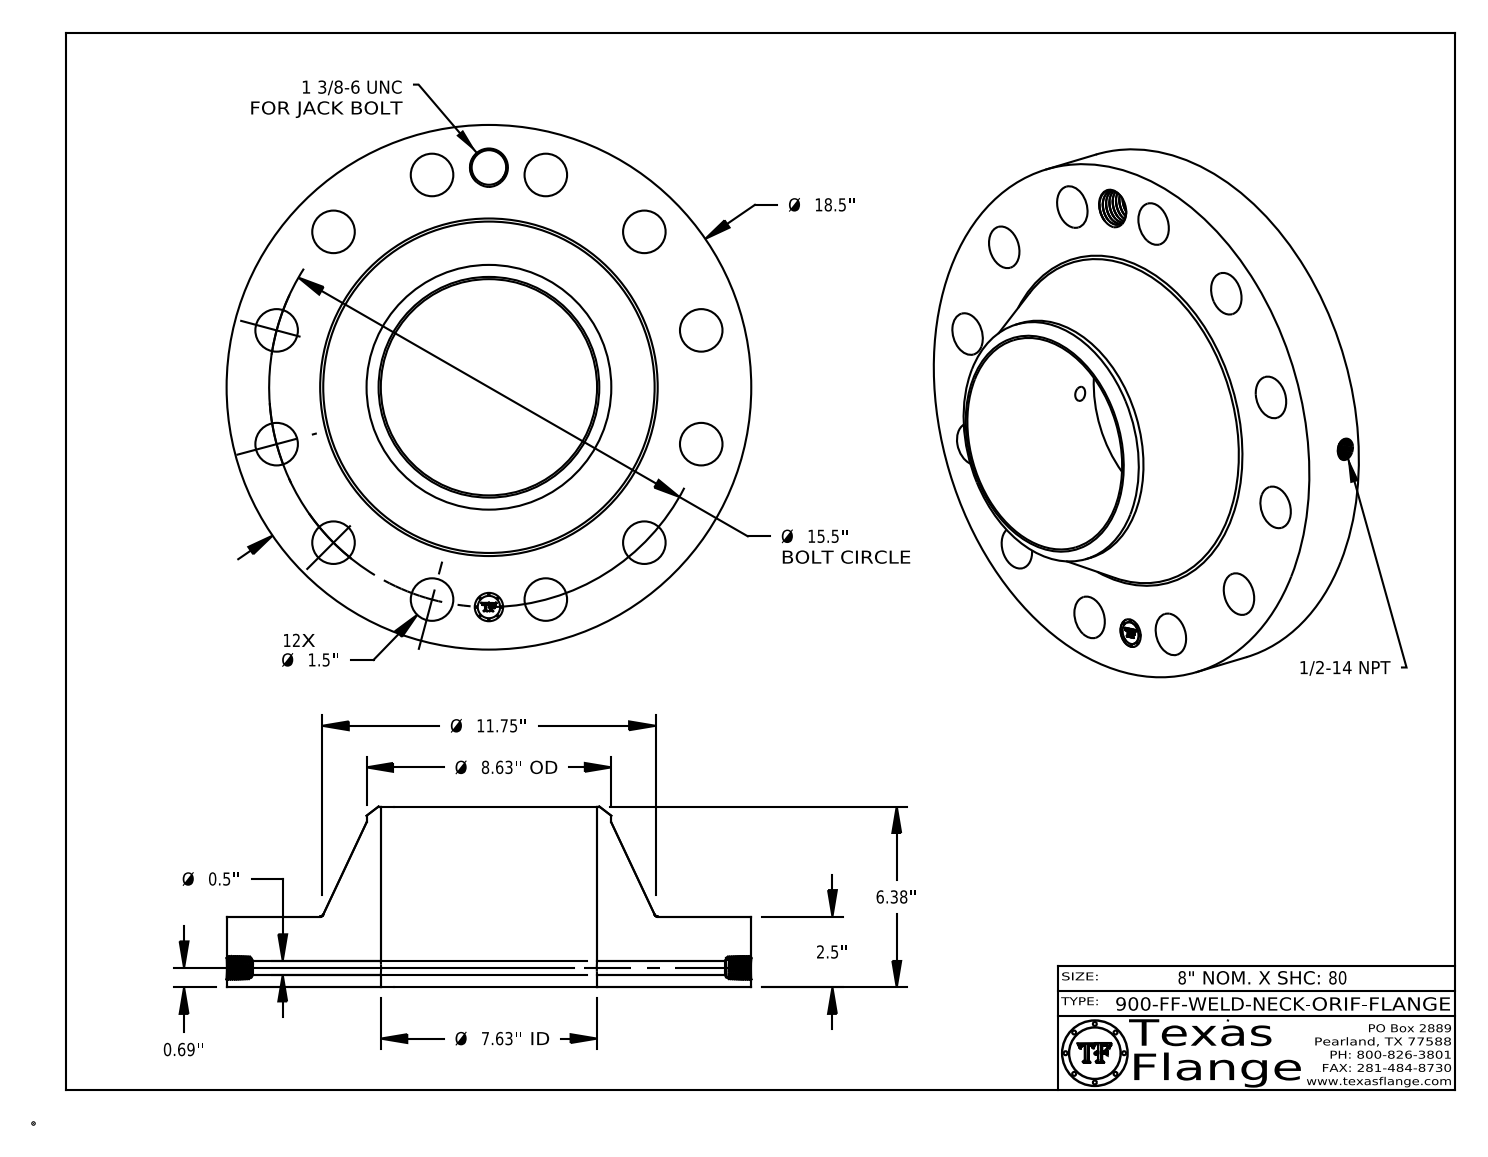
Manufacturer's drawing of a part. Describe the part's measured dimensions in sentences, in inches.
The part is named "900-FF-WELD-NECK". Its 3-D file was written by "CATIA V5 STEP AP214 (AUTOMOTIVE_DESIGN)". It is 1 solid with 774 faces: 368 planar, 100 cylindrical and 306 other. Overall it measures 18.5 by 18.5 by 6.38 inches. Its volume is 625.6 cubic inches and its surface area 951.3 square inches. Round holes: 12 of diameter 1.5, 1 of diameter 0.5, 1 of diameter 0.672, 1 of diameter 1, 1 of diameter 1.219, 1 of diameter 7.625. Round bosses or shafts: 8 of diameter 0.061, 1 of diameter 18.5, 1 of diameter 8.63, 1 of diameter 0.788. The main face-to-face distances are 2.5, 6.38, 3.88, 2.485, 0.015, 3.895, 0.298, 0.293, 0.054, 0.248. The hole center spacings are 7.75, 13.423, 14.972, 4.011, 7.75, 10.96, 15.5, 2.023.
